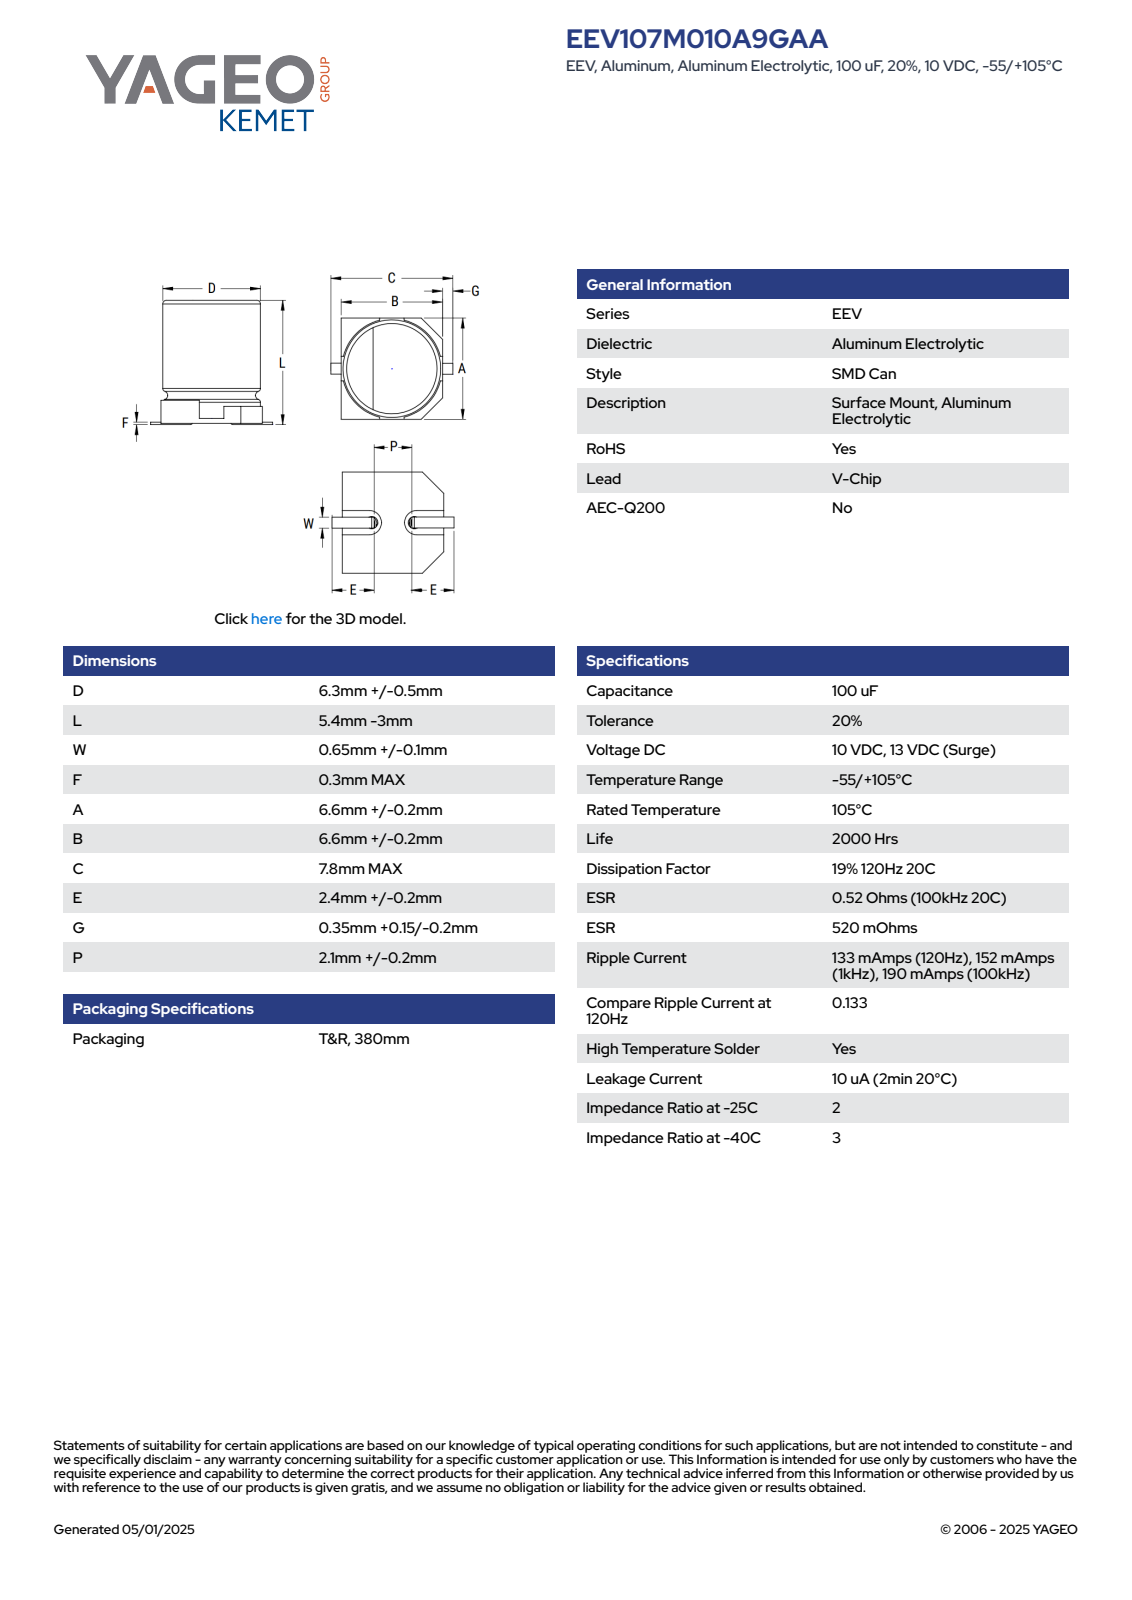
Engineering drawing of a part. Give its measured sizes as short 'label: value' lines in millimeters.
name: CAC_S_6.3X5.4_D6.8L5.65W0.75F0.3A6.8B6.8C7.8E2.8P2
written by: SolidWorks 2021 (AUTOMOTIVE_DESIGN)
unit: mm
bodies: 5 solids, 78 faces (61 planar, 11 cylindrical, 6 other)
size: 7.5 × 6.8 × 2.4
volume: 75 mm³; area: 217 mm²
bosses: 1× ⌀6.5
rounds: 2× R0.2, 1× R2.7, 1× R3.4
face distances: 2.1, 1.98, 1.5, 0.6, 0.48, 0.9, 0.42, 2.4, 6.8, 0.7
